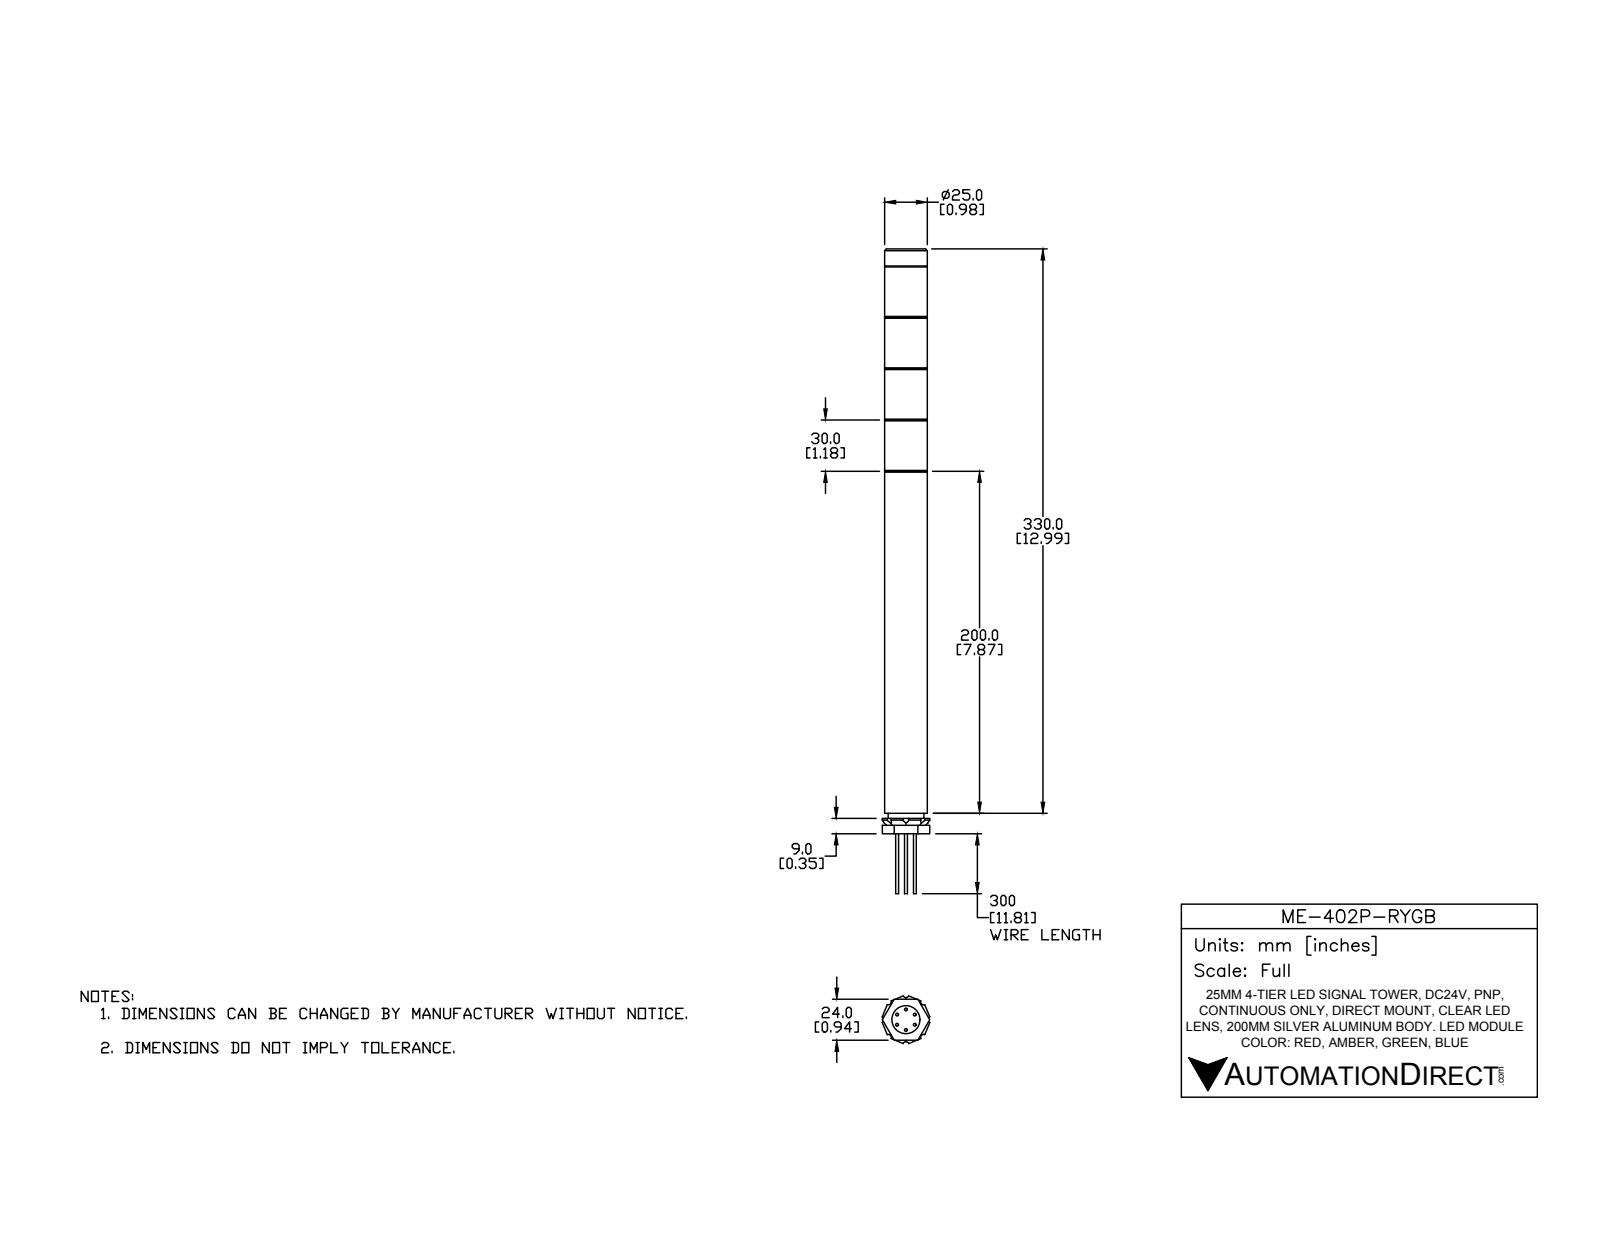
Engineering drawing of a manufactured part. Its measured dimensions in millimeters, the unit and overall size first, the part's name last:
Units: millimetres
Overall size (bounding box): 377 × 27.89 × 27.89
Round holes (diameter × count): ⌀3.2 ×1, ⌀7.7 ×1, ⌀16.4 ×1, ⌀18 ×1, ⌀20.7 ×1, ⌀21 ×1
Round bosses / shafts (diameter × count): ⌀1.7 ×6, ⌀25 ×1, ⌀20.9 ×1, ⌀16 ×1, ⌀5 ×1
Partial cylindrical surfaces — rounded edges, fillets, slot ends (radius × count): R1.75 ×8
Main face-to-face distances: 30, 60, 90, 120, 40, 297, 167, 197, 227, 257
Volume: 156 335 mm³ · Surface area: 41 143 mm²
Bodies: 15 solids, 156 faces (77 planar, 53 cylindrical, 26 other)
Part name (STEP PRODUCT): ME-402P-RYGB
STEP written by: SolidWorks 2016 (AUTOMOTIVE_DESIGN)
